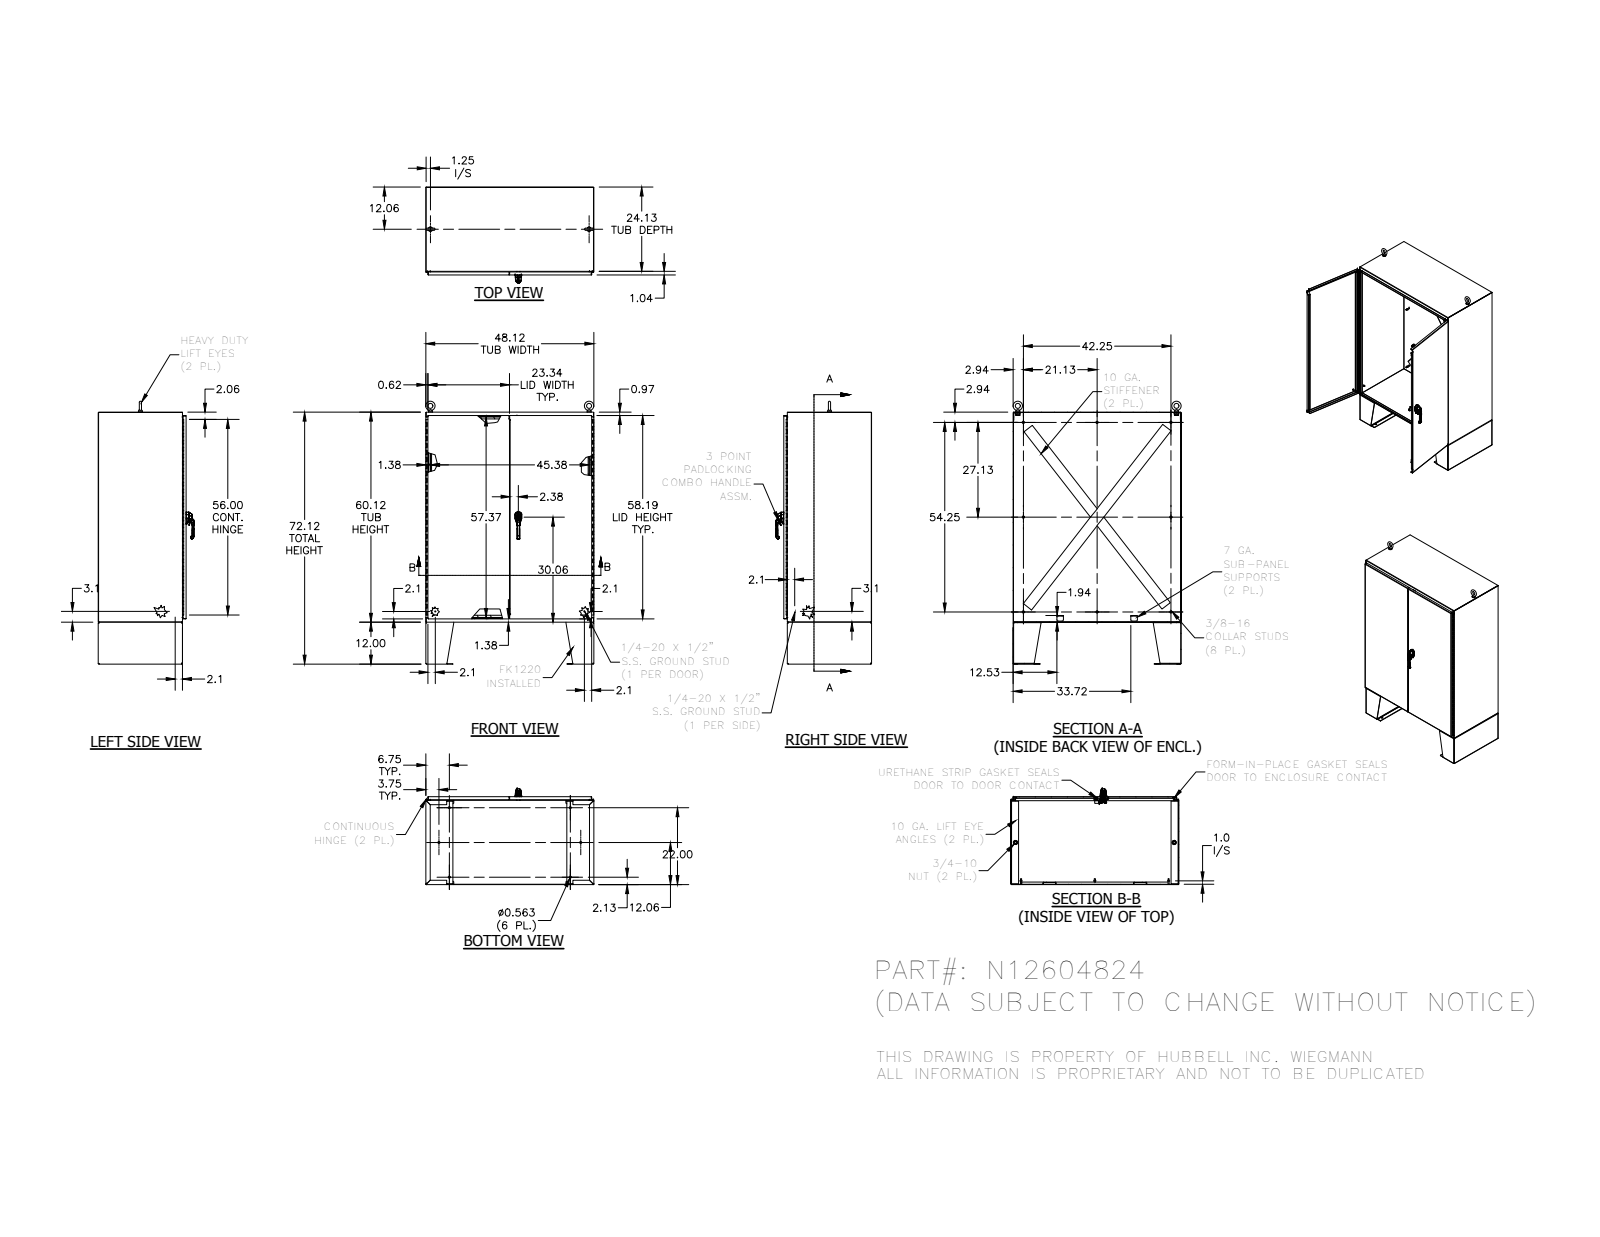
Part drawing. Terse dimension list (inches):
name: N12604824
written by: SolidWorks 2018 (AUTOMOTIVE_DESIGN)
unit: in
bodies: 76 solids, 2400 faces (1384 planar, 716 cylindrical, 300 other)
size: 75.248 × 48.125 × 27.338
volume: 1 453 in³; area: 29 011 in²
holes: 18× ⌀0.563, 8× ⌀0.277, 4× ⌀0.2, 3× ⌀0.125, 3× ⌀0.28, 2× ⌀0.241, 2× ⌀0.25, 2× ⌀0.252, 2× ⌀0.4, 2× ⌀0.45, 2× ⌀0.642, 2× ⌀0.813
bosses: 8× ⌀0.33, 6× ⌀0.625, 5× ⌀0.25, 3× ⌀0.337, 2× ⌀1.25, 2× ⌀1.12, 2× ⌀1, 2× ⌀0.75
rounds: 24× R0.031, 23× R0.094, 22× R0.219, 18× R0.05, 16× R0.025, 15× R0.125, 13× R0.03, 8× R0.067
face distances: 0.094, 25.067, 48.031, 24.973, 25.16, 60.031, 48.125, 47.938, 0.125, 59.938
hole spacings: 2.041, 5, 10.38, 11.313, 22.75, 23.293, 34.405, 38.915
